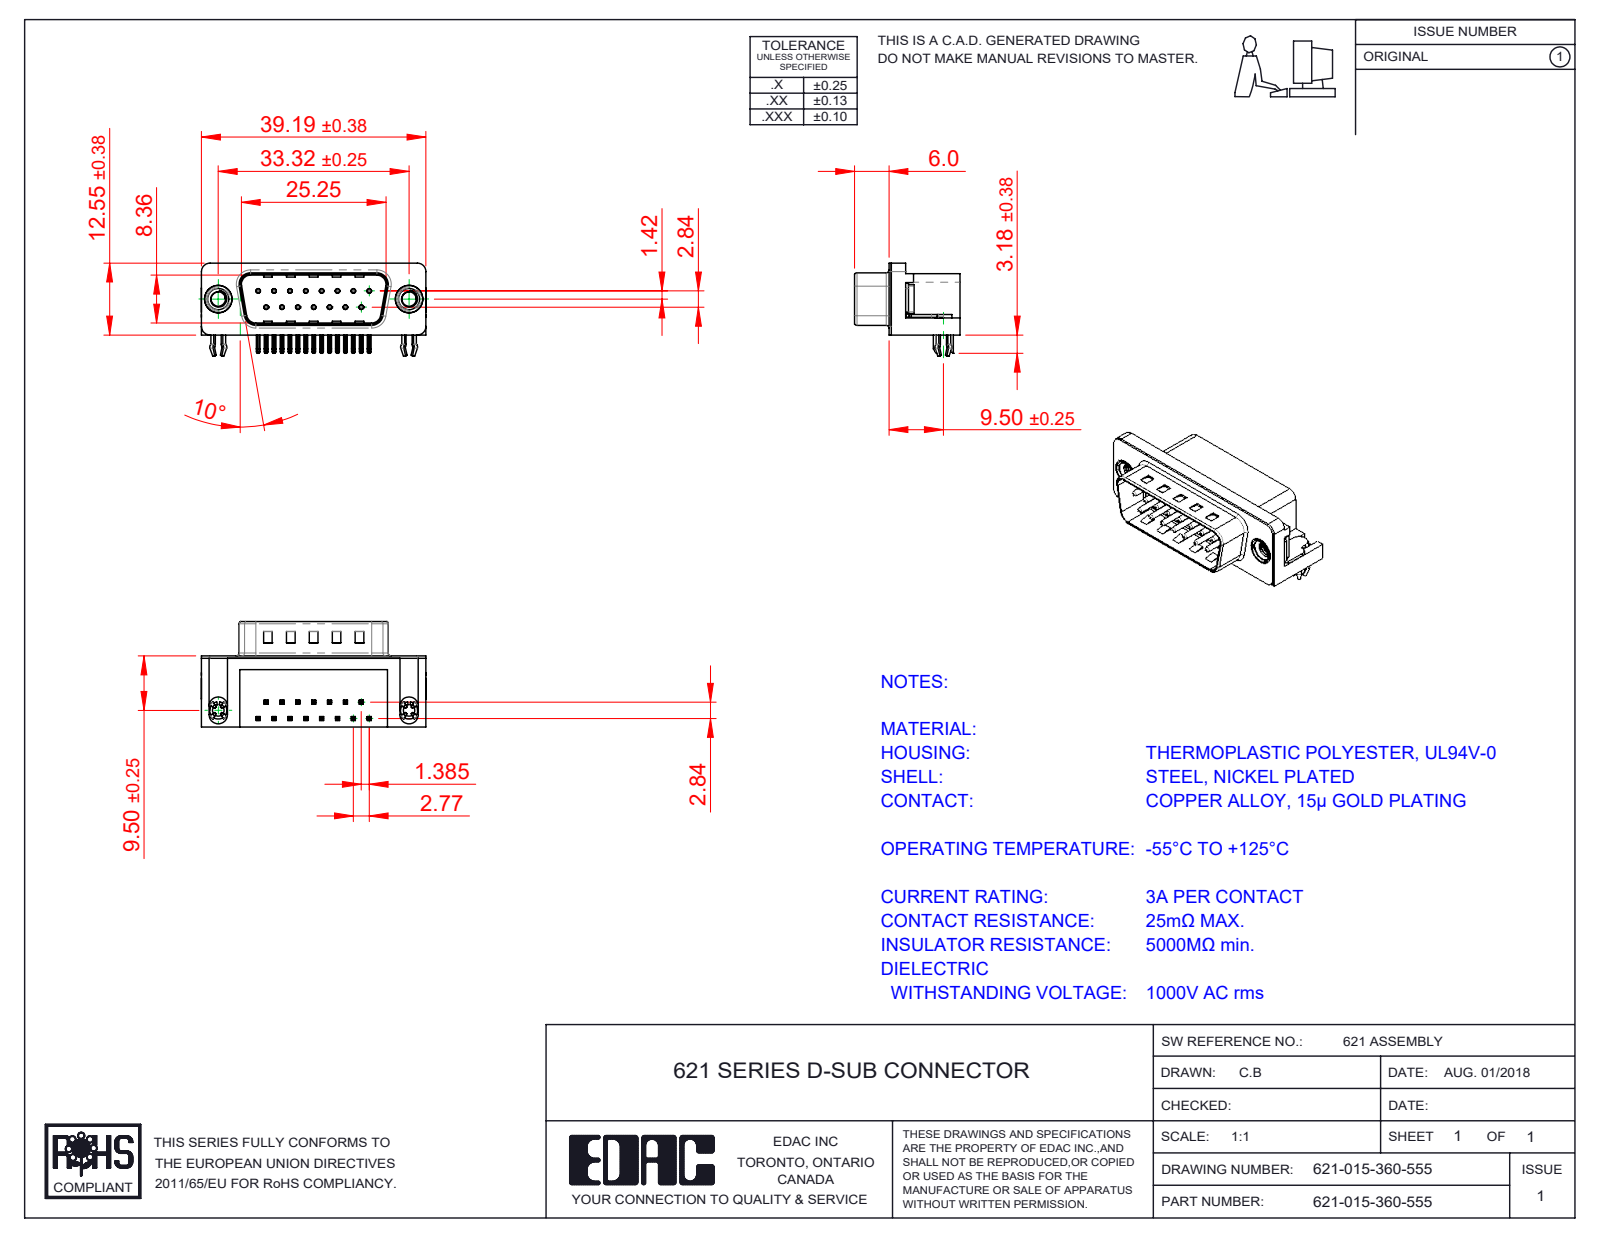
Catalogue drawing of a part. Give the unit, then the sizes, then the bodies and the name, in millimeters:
Units: millimetres
Overall size (bounding box): 39.22 × 18.4 × 15.73
Round holes (diameter × count): ⌀0.35 ×15, ⌀0.8 ×15, ⌀2.26 ×2, ⌀2.5 ×2, ⌀4 ×2, ⌀4.8 ×2, ⌀5 ×2
Round bosses / shafts (diameter × count): ⌀0.75 ×15, ⌀4.9 ×2, ⌀4.75 ×2, ⌀3.9 ×2, ⌀3.26 ×2
Partial cylindrical surfaces — rounded edges, fillets, slot ends (radius × count): R0.25 ×68, R0.12 ×30, R1 ×16, R0.5 ×9, R1.6 ×8, R1.5 ×6, R0.9 ×4, R2 ×4
Main face-to-face distances: 0.4, 12, 10.35, 2.1, 10.46, 12.4, 1.7, 10.86, 8.76, 2.9
Hole centre spacings: 3.16, 2.77, 5.54, 8.31, 11.08, 5.03, 5.04, 7.48
Volume: 4 421 mm³ · Surface area: 5 733 mm²
Bodies: 21 solids, 1507 faces (893 planar, 461 cylindrical, 153 other)
Part name (STEP PRODUCT): 621 Contact Top; 621 Housing_15 Socket; 621 Contact Bottom; 621 M3 Threaded Rivet (+3 more)
STEP written by: SolidWorks 2016 (CONFIG_CONTROL_DESIGN)
